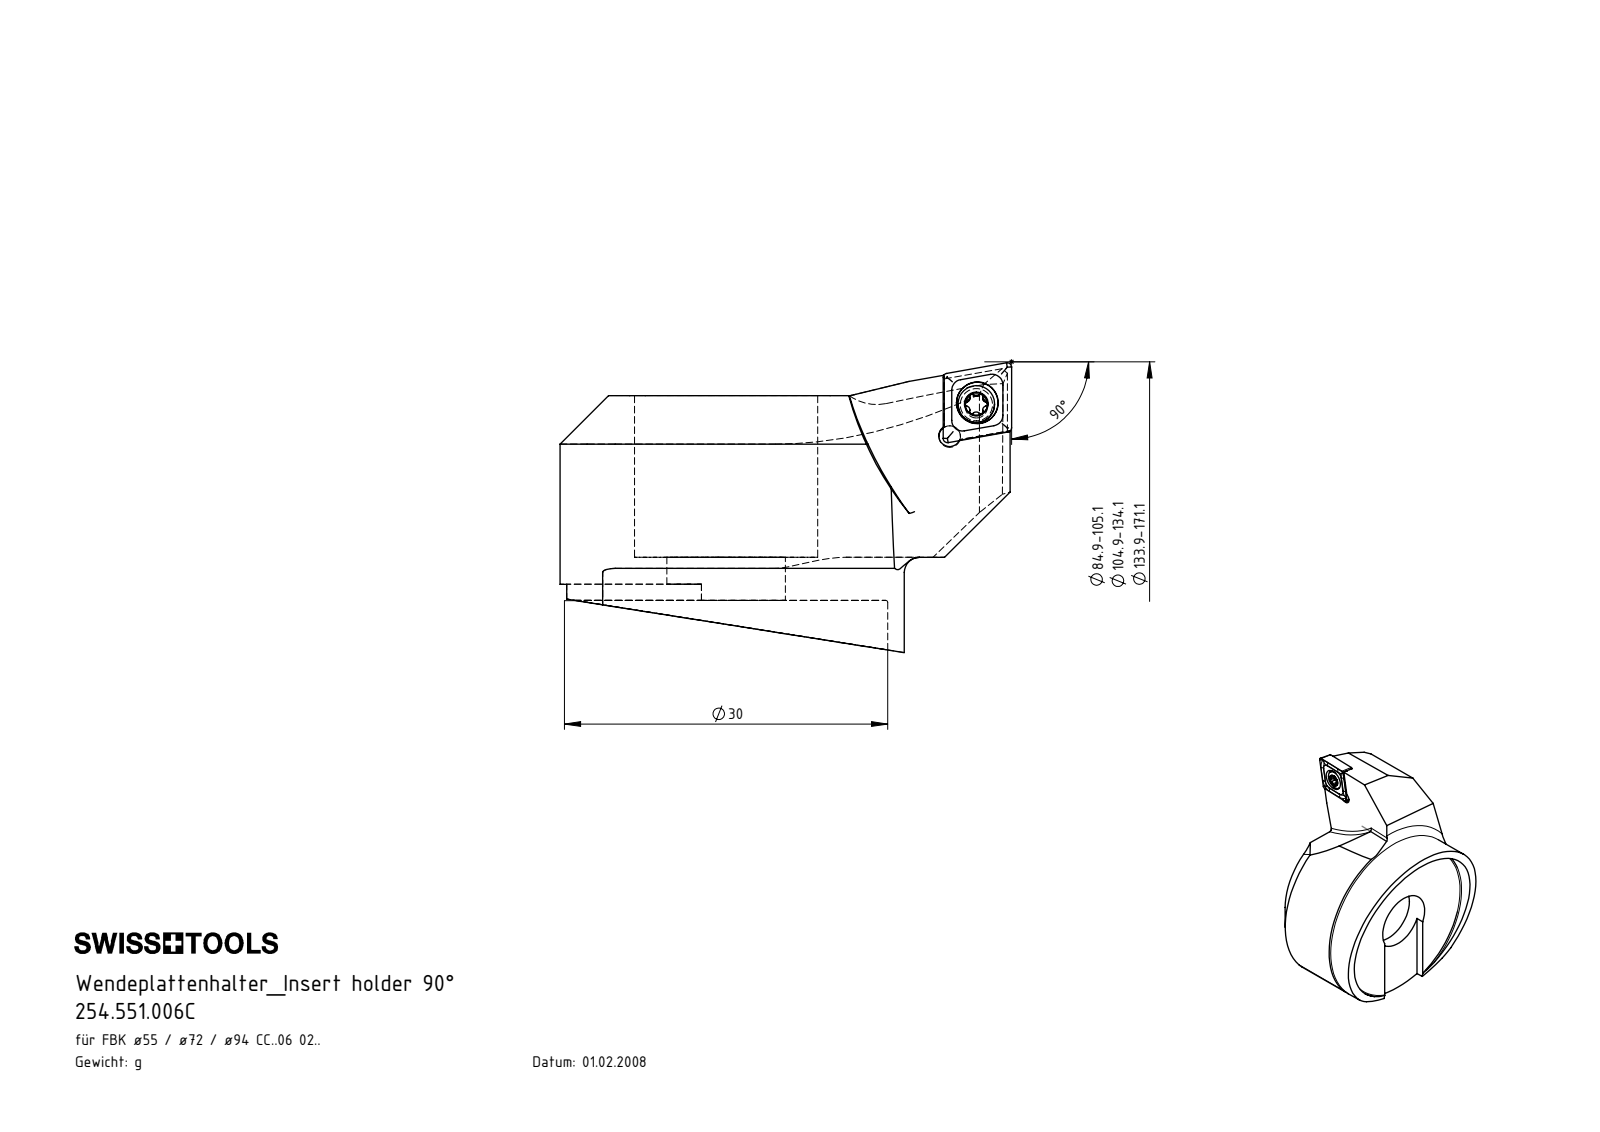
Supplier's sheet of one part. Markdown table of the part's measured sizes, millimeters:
| quantity | value |
| --- | --- |
| part name | F55-WCA.001.022_D_fertigbearbeitet; CCMT060204; 254.551.006C; WCA-ER2.001.006_A |
| STEP written by | SolidWorks 2017 (CONFIG_CONTROL_DESIGN) |
| units | millimeters |
| bodies | 5 solids, 161 faces (50 planar, 51 cylindrical, 60 other) |
| overall size | 41.9 × 33.2 × 26.89 |
| volume | 13 693 mm³ |
| surface area | 5 984 mm² |
| round holes (diameter × count) | 2 × 1, 2.05 × 1, 2.8 × 1, 3.85 × 1, 11 × 1, 17 × 1, 30 × 1 |
| round bosses / shafts (diameter × count) | 3.4 × 1, 2.5 × 1 |
| partial cylindrical surfaces (radius × count) | 0.21 × 6, 0.36 × 5, 0.5 × 2, 10 × 2, 0.36 × 1, 5 × 1, 16.55 × 1, 16.6 × 1 |
| main face-to-face distances | 19, 1, 18, 15, 14, 4, 1.5, 17.5, 16.5, 2.5 |
| hole center spacings | 3.86, 4.01 |
